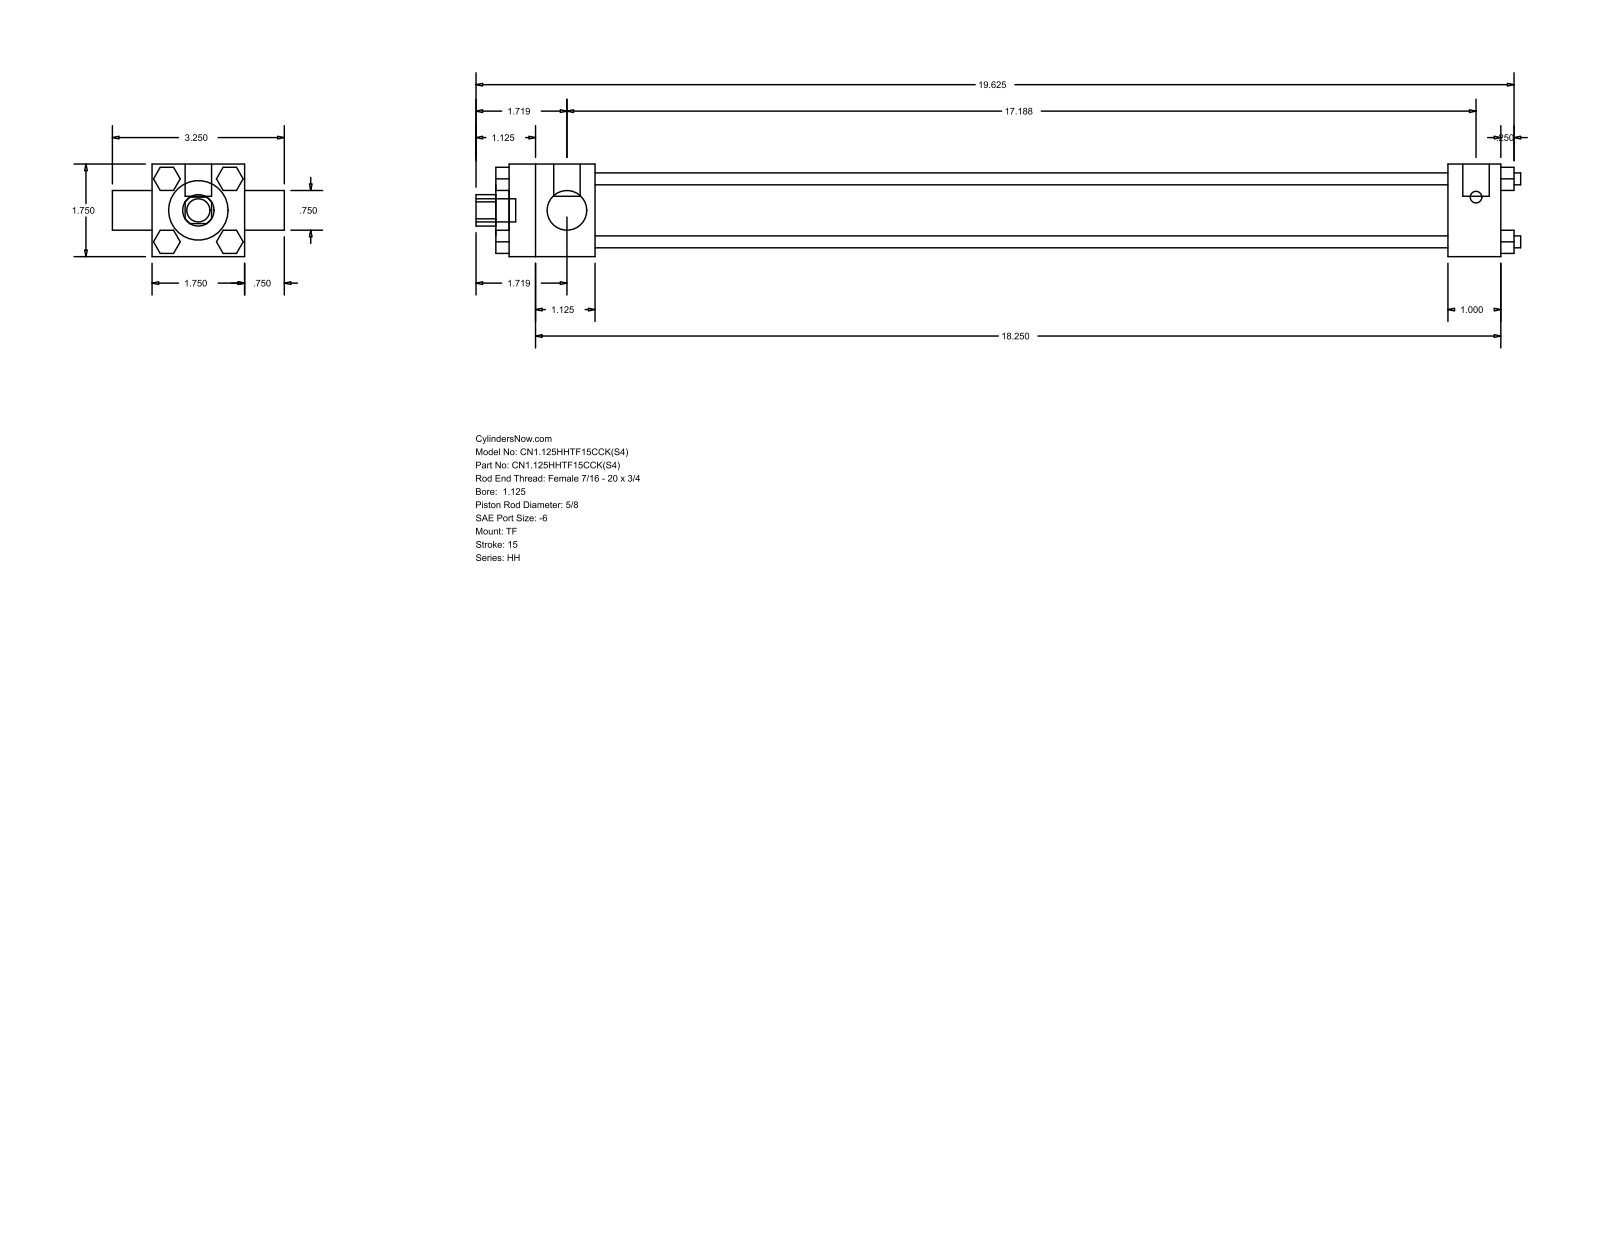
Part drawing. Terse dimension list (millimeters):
name: HH_TF__0112_0.625
written by: GSSL Pune (CONFIG_CONTROL_DESIGN)
unit: mm
bodies: 0 solids, 120 faces (92 planar, 28 cylindrical, 0 other)
size: 501.65 × 82.55 × 44.45
holes: 1× ⌀15.88, 1× ⌀19.05, 1× ⌀28.57, 1× ⌀34.92
bosses: 4× ⌀5.71, 3× ⌀5.56, 2× ⌀12.7, 1× ⌀11.11
rounds: 1× R7.54
face distances: 44.46, 11.11, 409.58, 434.97, 25.39, 41.27, 450.85, 476.24, 47.62, 6.35
